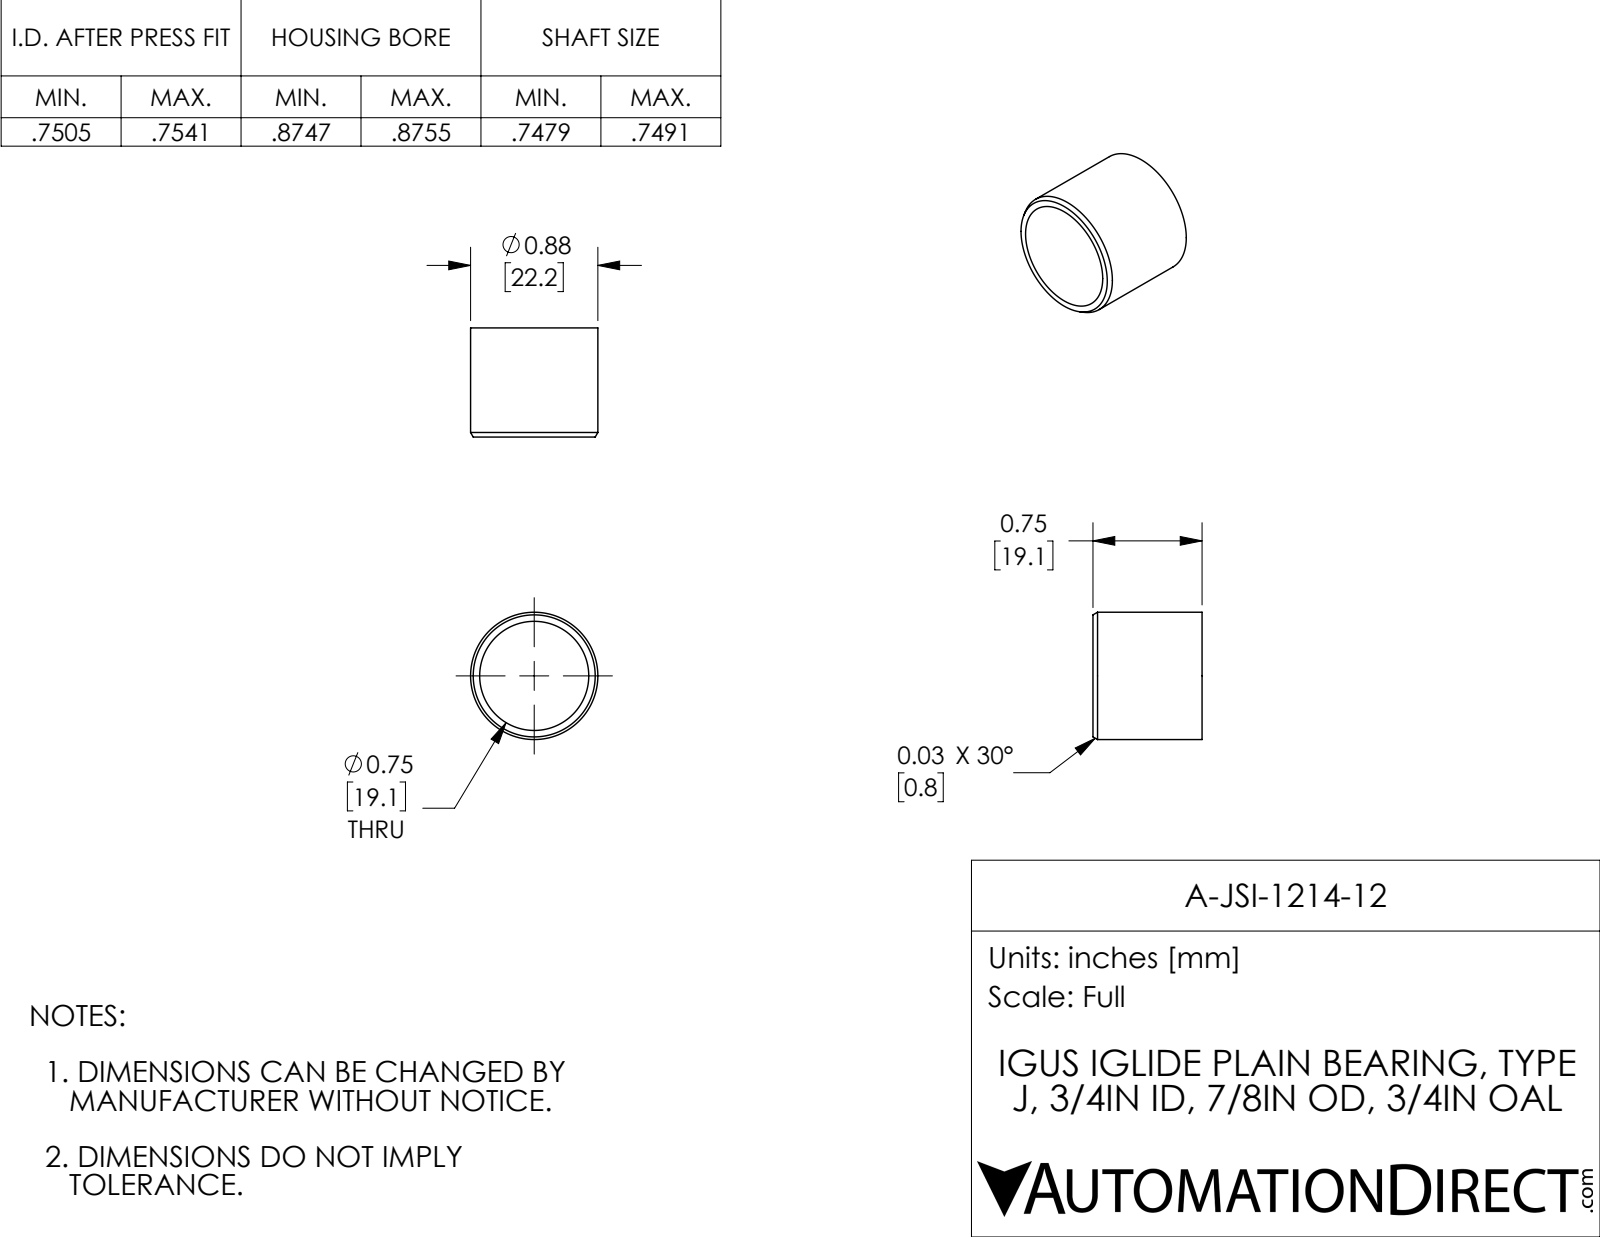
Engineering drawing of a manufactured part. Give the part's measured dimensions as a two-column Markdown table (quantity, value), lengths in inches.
| quantity | value |
| --- | --- |
| part name | A-JSI-1214-12 |
| STEP written by | SolidWorks 2017 (AUTOMOTIVE_DESIGN) |
| units | inches |
| bodies | 1 solid, 10 faces (2 planar, 4 cylindrical, 4 other) |
| overall size | 0.875 × 0.875 × 0.75 |
| volume | 0.119 in³ |
| surface area | 4.091 in² |
| round holes (diameter × count) | 0.75 × 1 |
| round bosses / shafts (diameter × count) | 0.875 × 1 |
| main face-to-face distances | 0.75 |
